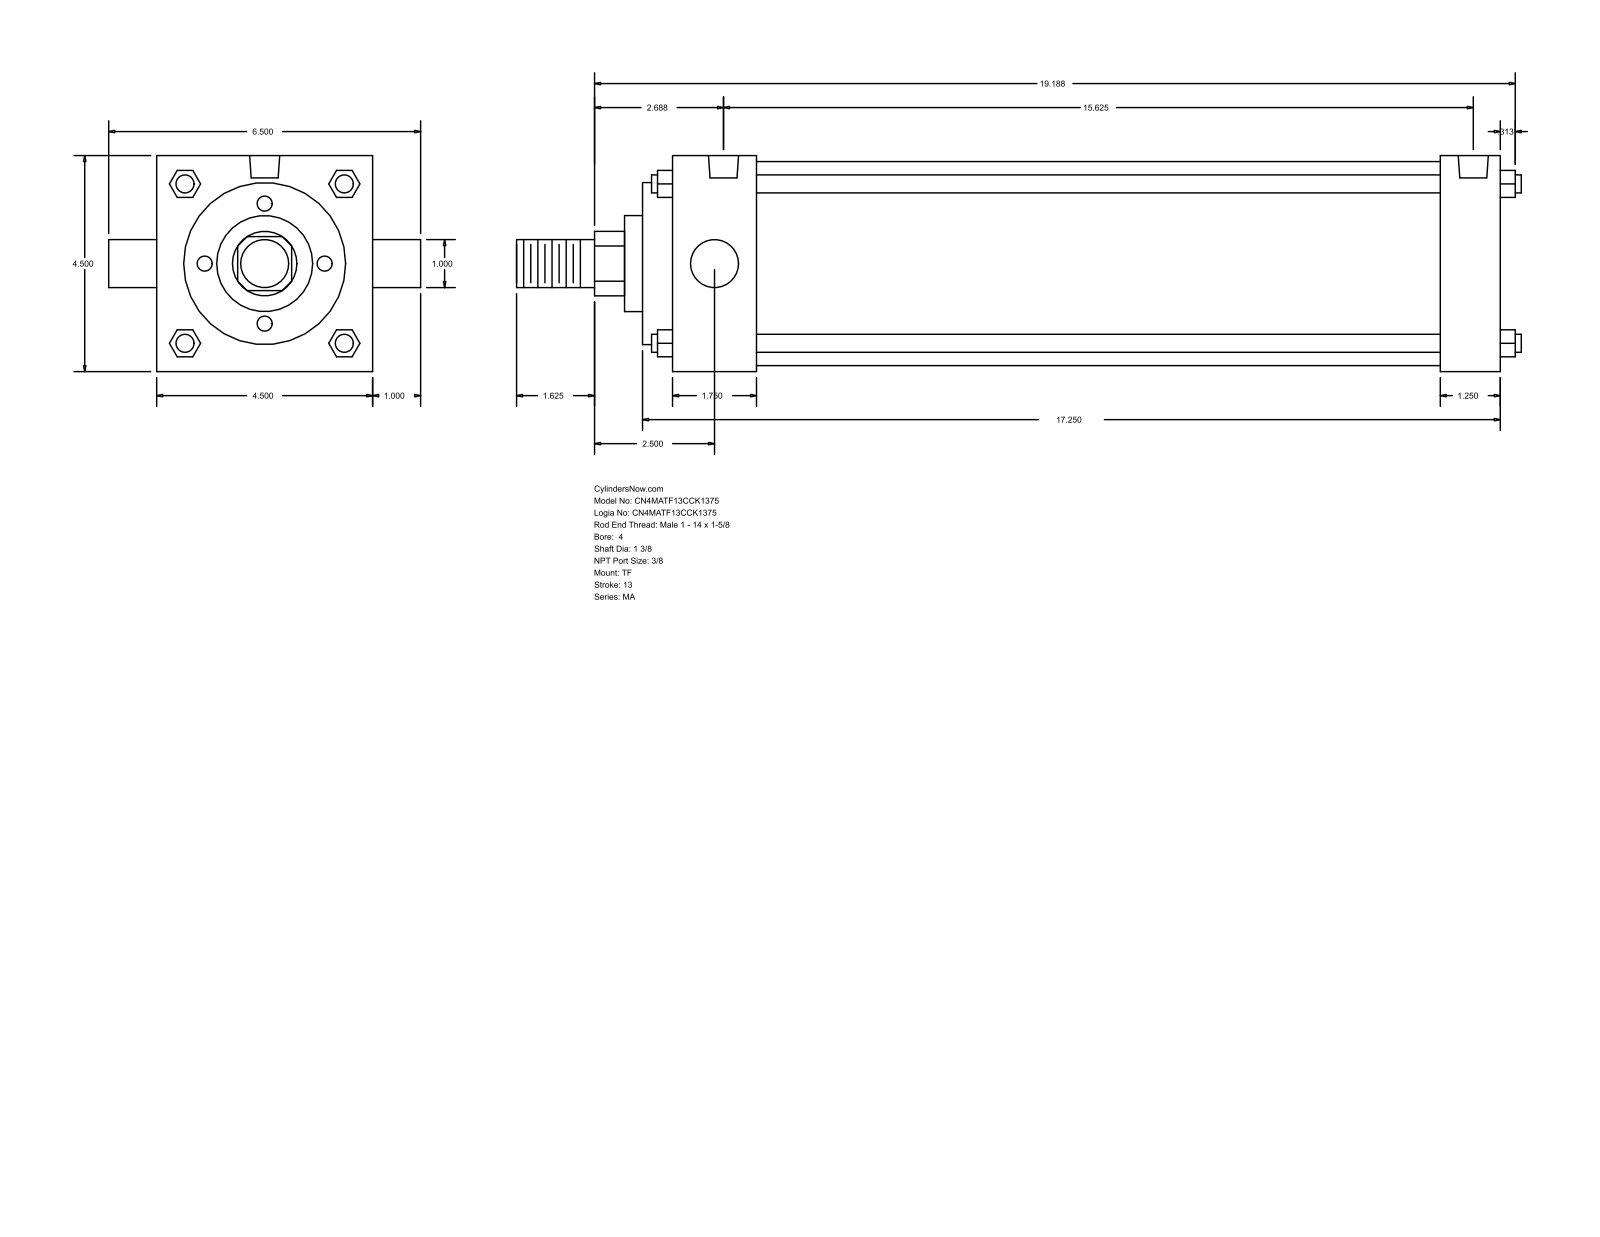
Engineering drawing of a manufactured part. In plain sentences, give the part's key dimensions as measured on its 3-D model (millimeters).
The part is named "MA_TF__0400_1.375". Its 3-D file was written by "GSSL Pune (CONFIG_CONTROL_DESIGN)". It is 0 solids with 122 faces: 93 planar, 29 cylindrical and 0 other. Overall it measures 531.81 by 165.1 by 114.3 millimeters. Round holes: 3 of diameter 11.11, 2 of diameter 15.93. Round bosses or shafts: 4 of diameter 9.53, 2 of diameter 25.4, 1 of diameter 107.95, 1 of diameter 85.72, 1 of diameter 50.8, 1 of diameter 34.92. Partial cylindrical surfaces (rounded edges, fillets, slot ends): 1 of radius 17.06. The main face-to-face distances are 114.3, 438.16, 15.87, 454.03, 422.28, 406.41, 31.75, 60.32, 44.45, 361.96. The hole center spacings are 4.76, 4.77, 387.35, 392.11, 392.12, 396.88.
